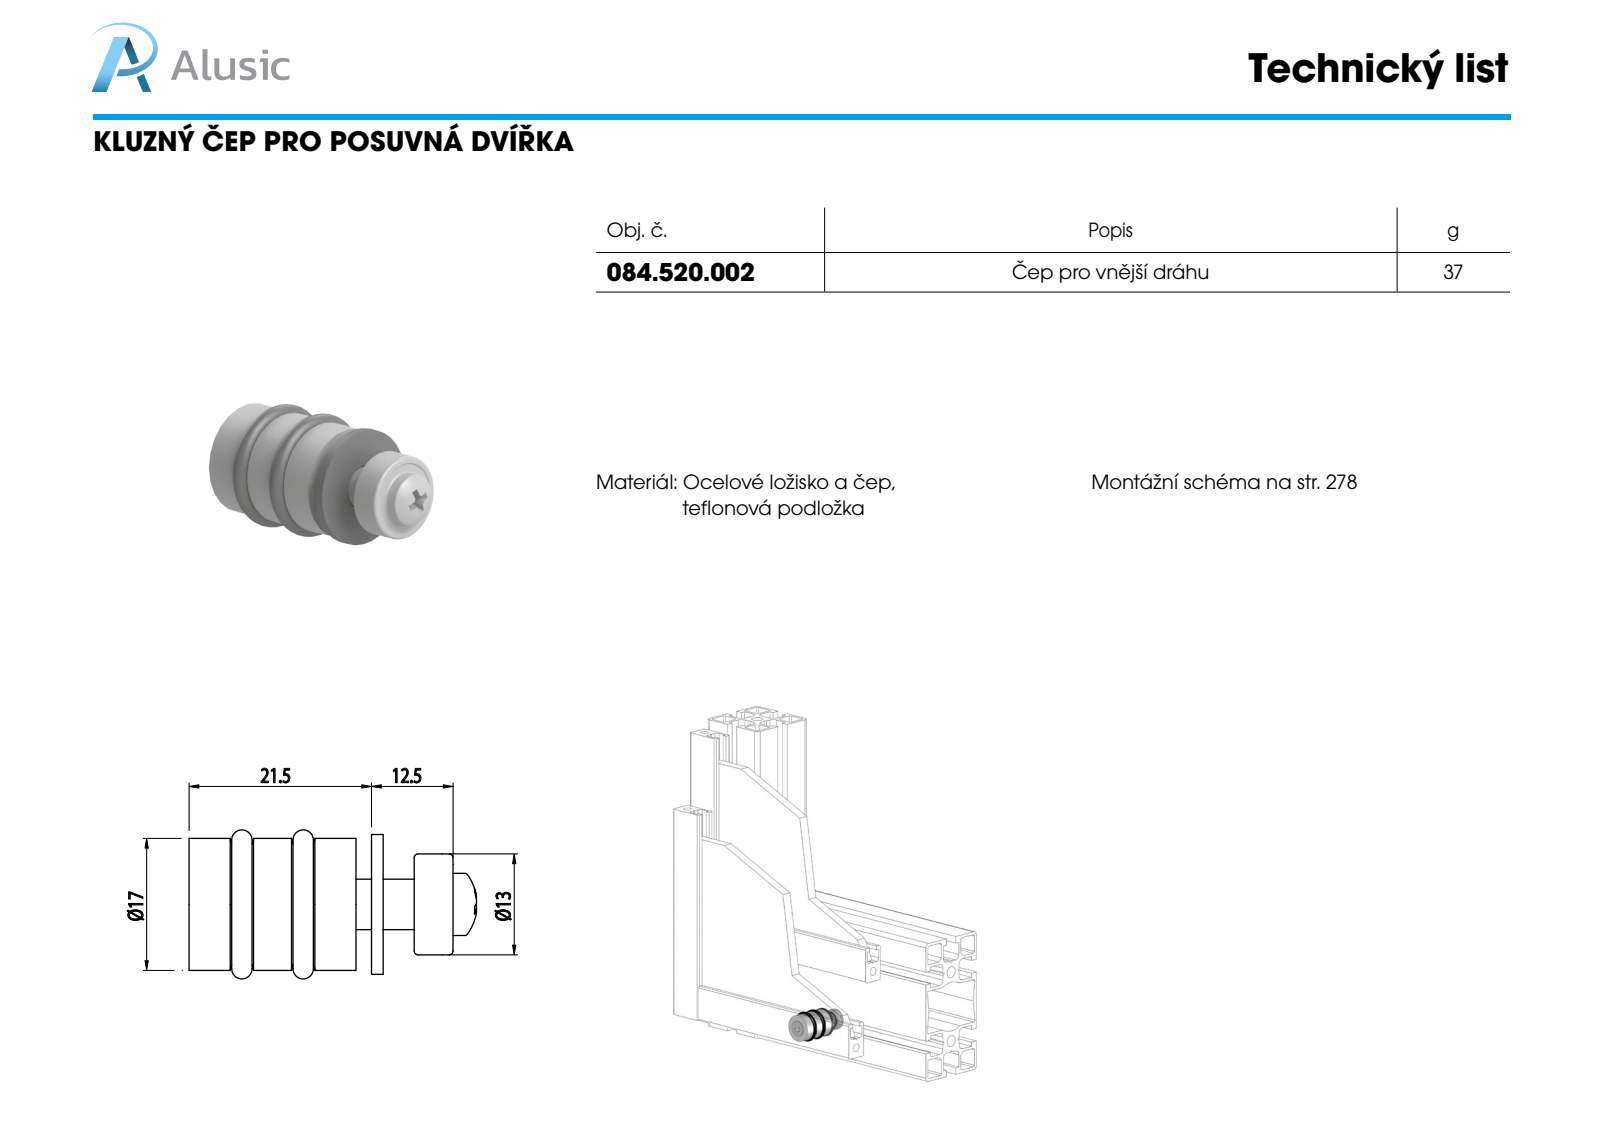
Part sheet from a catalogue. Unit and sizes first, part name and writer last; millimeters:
Units: millimetres
Overall size (bounding box): 37.02 × 19.19 × 19.19
Round holes (diameter × count): ⌀3.3 ×1, ⌀6 ×1, ⌀6.8 ×1, ⌀7 ×1
Round bosses / shafts (diameter × count): ⌀18 ×1, ⌀17 ×1, ⌀13 ×1, ⌀8 ×1, ⌀6.5 ×1, ⌀4 ×1
Main face-to-face distances: 1.5, 2, 3.5, 21.5, 23.5, 25, 4.5, 34, 12.5, 10.5
Volume: 5 675 mm³ · Surface area: 4 656 mm²
Bodies: 6 solids, 148 faces (30 planar, 40 cylindrical, 78 other)
Part name (STEP PRODUCT): 084.520.002; RT; 700027; GUARNIZIONI OR_OR-3056 (+2 more)
STEP written by: SolidWorks 2011 (CONFIG_CONTROL_DESIGN)
